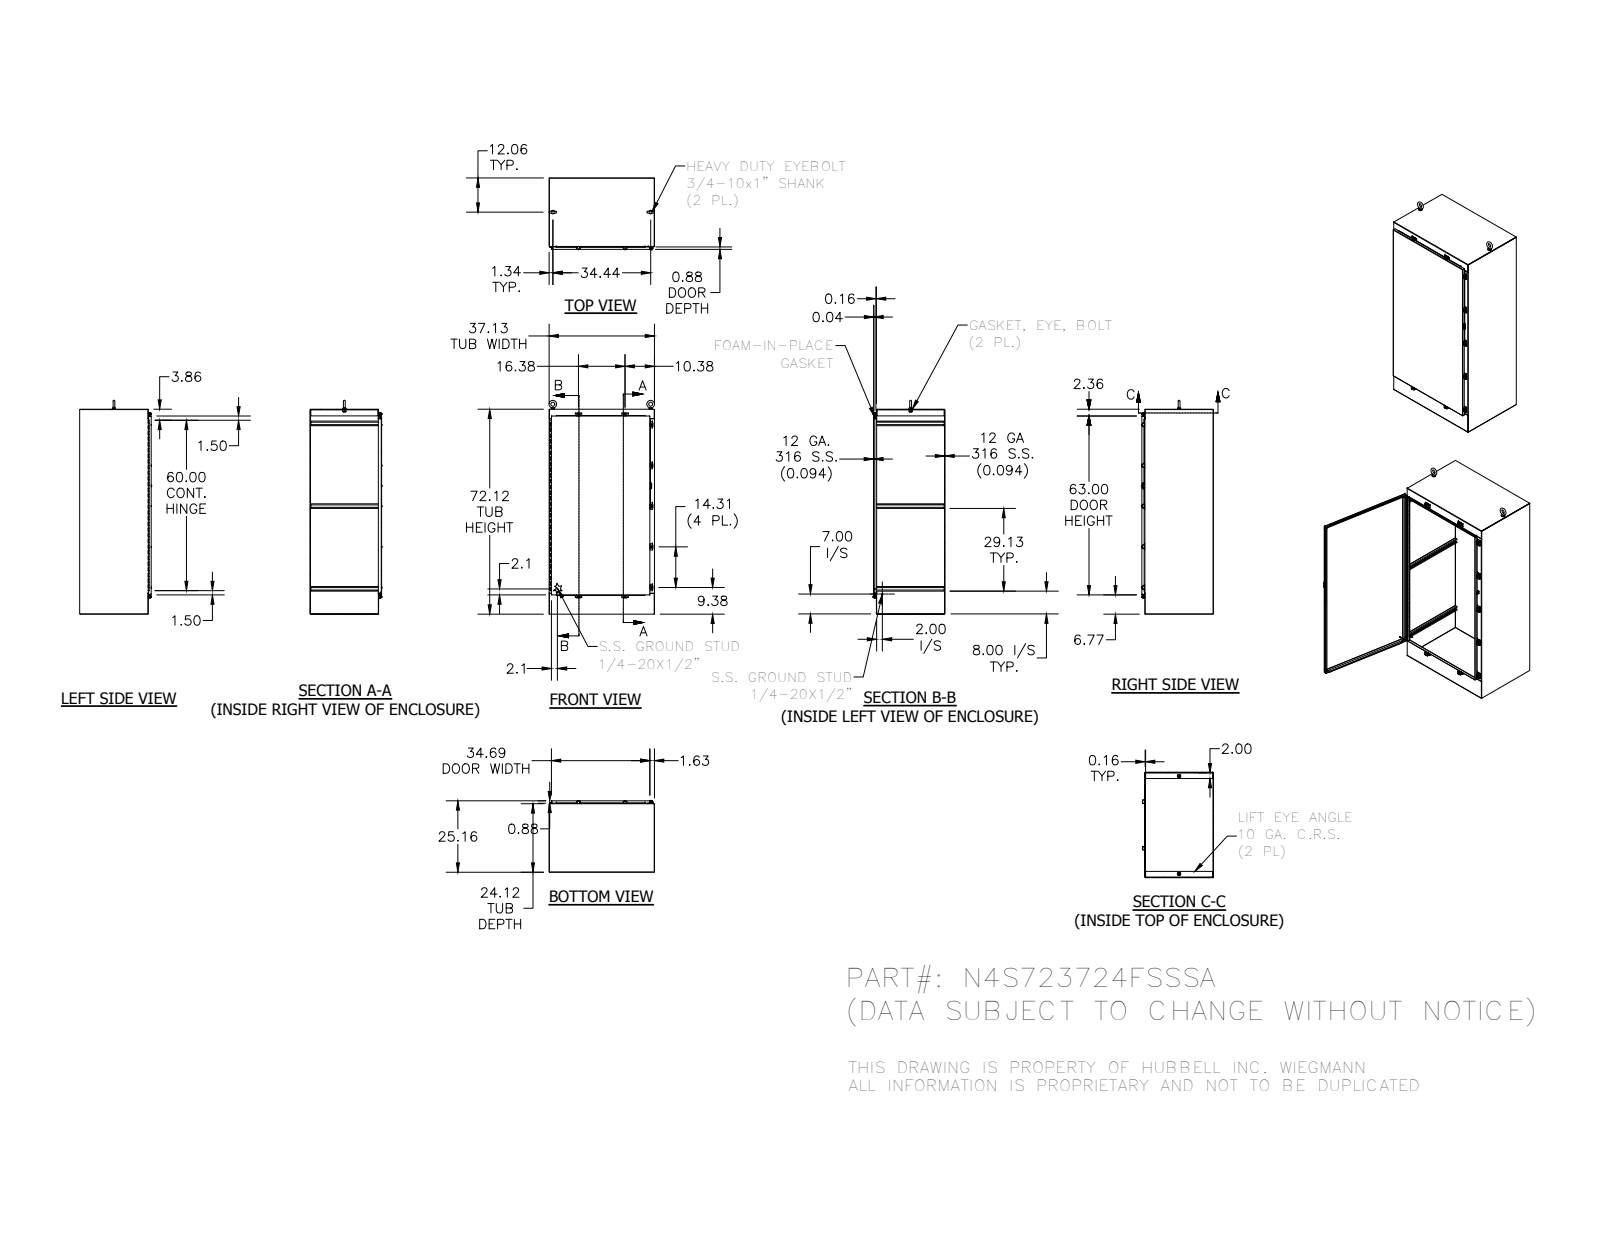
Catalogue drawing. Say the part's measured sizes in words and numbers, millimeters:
The part is named "38413_1; 30823_1; HSSN1300W60_1; N4S723724FSSSABTM_1 (+8 more)". Its 3-D file was written by "SolidWorks 2014 (AUTOMOTIVE_DESIGN)". It is 78 solids with 3000 faces: 1210 planar, 1210 cylindrical and 580 other. Overall it measures 1911.3 by 943 by 644 millimeters. Its volume is 20 120 000 cubic millimeters and its surface area 16 350 000 square millimeters. Round holes: 9 of diameter 5.4, 9 of diameter 7.1, 9 of diameter 7.6, 3 of diameter 2.8, 2 of diameter 16.3, 2 of diameter 20.7, 1 of diameter 3.2, 1 of diameter 4, 1 of diameter 12.7. Round bosses or shafts: 12 of diameter 6.4, 9 of diameter 13.2, 9 of diameter 12.7, 9 of diameter 8.9, 2 of diameter 31.8, 2 of diameter 28.4, 2 of diameter 19.1, 2 of diameter 8.6. Partial cylindrical surfaces (rounded edges, fillets, slot ends): 107 of radius 0.8, 43 of radius 3.2, 22 of radius 1.6, 21 of radius 6.4, 19 of radius 0.8, 18 of radius 0.5, 18 of radius 1.3, 18 of radius 2.2. The main face-to-face distances are 2.4, 636.7, 940.6, 634.3, 639.1, 938.2, 1829.6, 943, 610.4, 26.3. The hole center spacings are 363.6, 727.1, 20, 416.1, 1090.7, 1635.1, 1687.2, 11.4.
